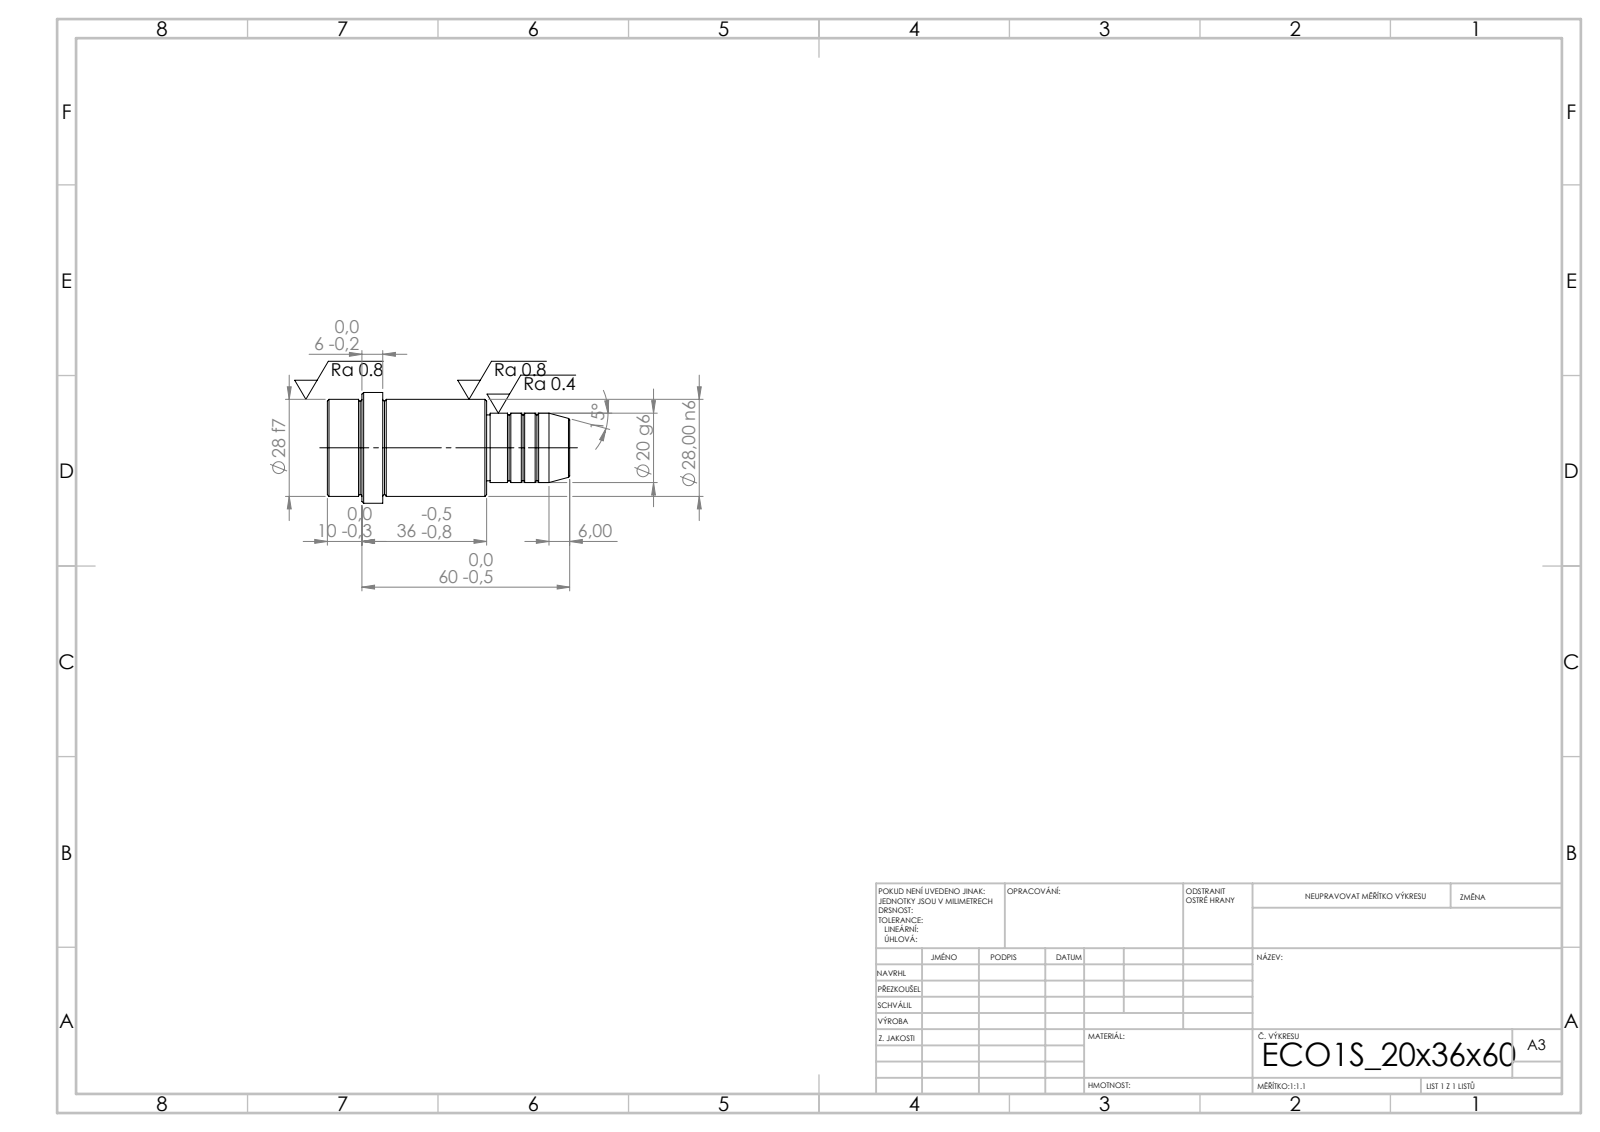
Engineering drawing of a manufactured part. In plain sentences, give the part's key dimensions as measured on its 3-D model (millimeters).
Its 3-D file was written by "SolidWorks 2019 (CONFIG_CONTROL_DESIGN)". It is 1 solid with 52 faces: 6 planar, 16 cylindrical and 30 other. Overall it measures 70 by 32 by 32 millimeters. Its volume is 36 502 cubic millimeters and its surface area 7 290 square millimeters. Round bosses or shafts: 1 of diameter 32, 1 of diameter 28, 1 of diameter 20, 1 of diameter 19. The main face-to-face distances are 46, 24, 70, 54, 30, 16, 60, 36, 6, 10.
